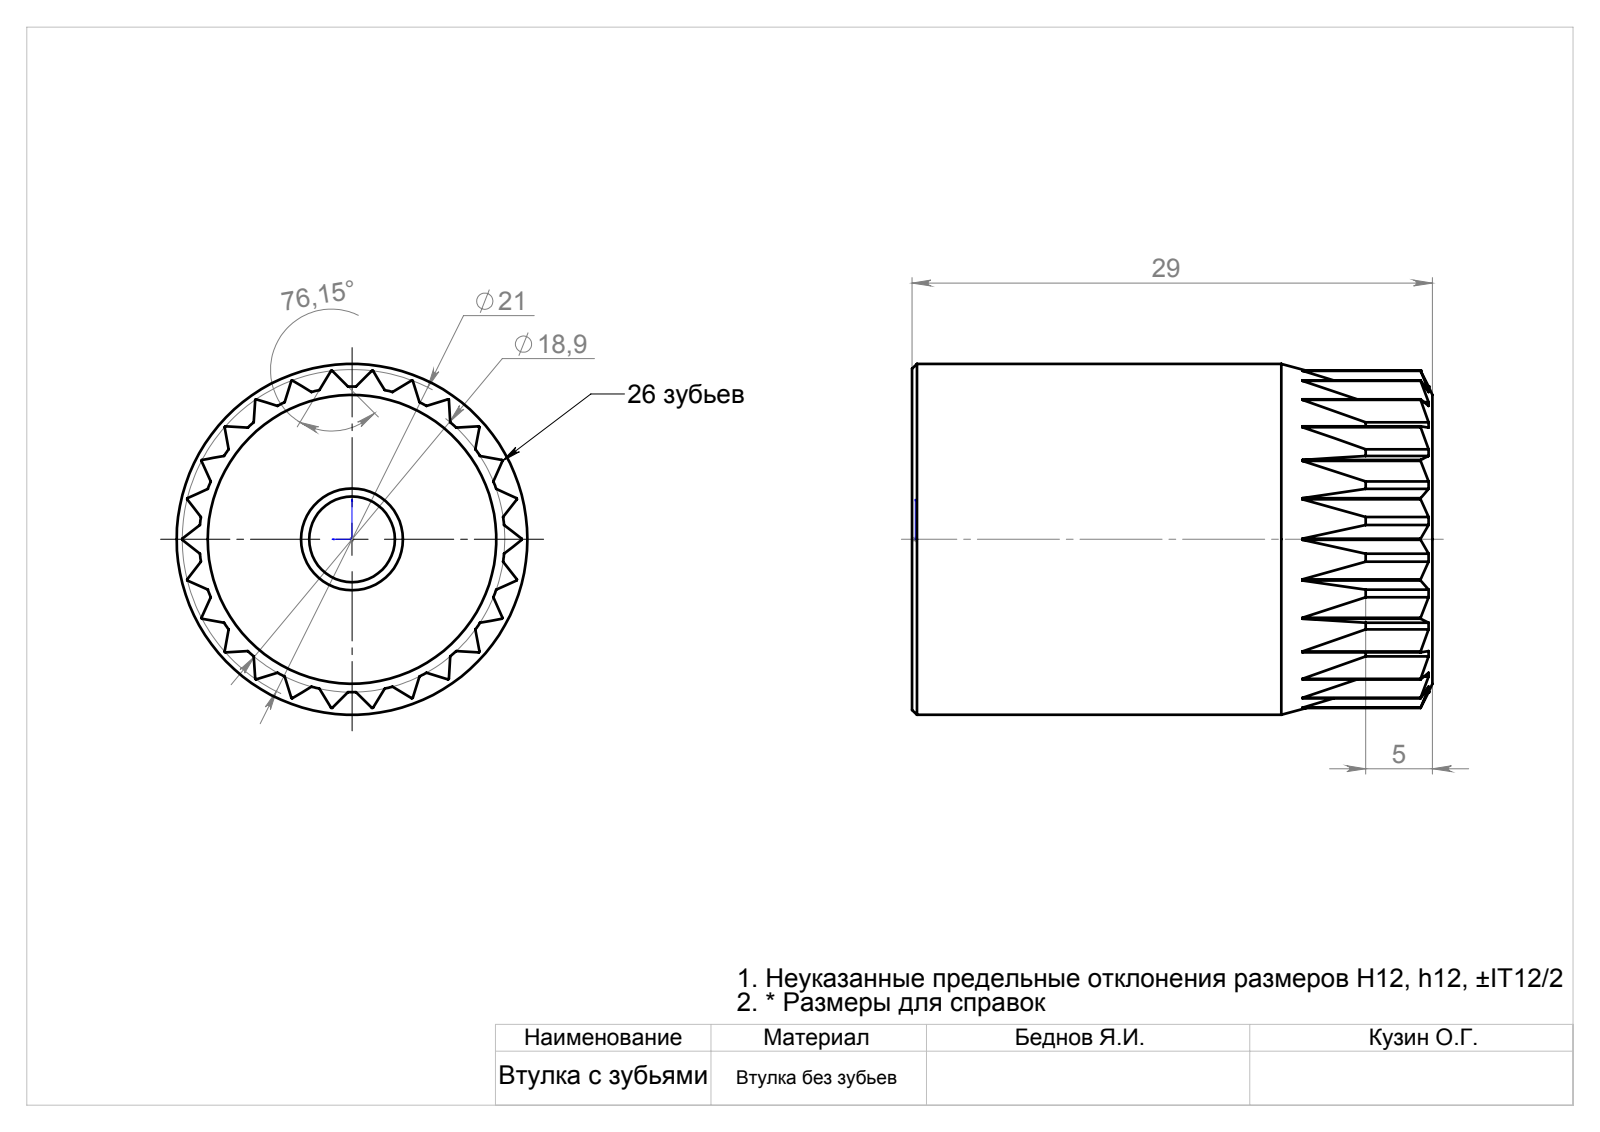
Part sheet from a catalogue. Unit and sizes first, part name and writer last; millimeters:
Units: millimetres
Overall size (bounding box): 32.2 × 21.7 × 21.7
Round holes (diameter × count): ⌀5.3 ×1, ⌀14.4 ×1
Round bosses / shafts (diameter × count): ⌀21.7 ×1
Partial cylindrical surfaces — rounded edges, fillets, slot ends (radius × count): R9.45 ×1, R10.5 ×1
Main face-to-face distances: 32.2, 13, 13.02
Volume: 7 047 mm³ · Surface area: 4 150 mm²
Bodies: 1 solid, 114 faces (54 planar, 55 cylindrical, 5 other)
Part name (STEP PRODUCT): Admi17DDra5j
STEP written by: UGS - NX 4.0 (CONFIG_CONTROL_DESIGN)
